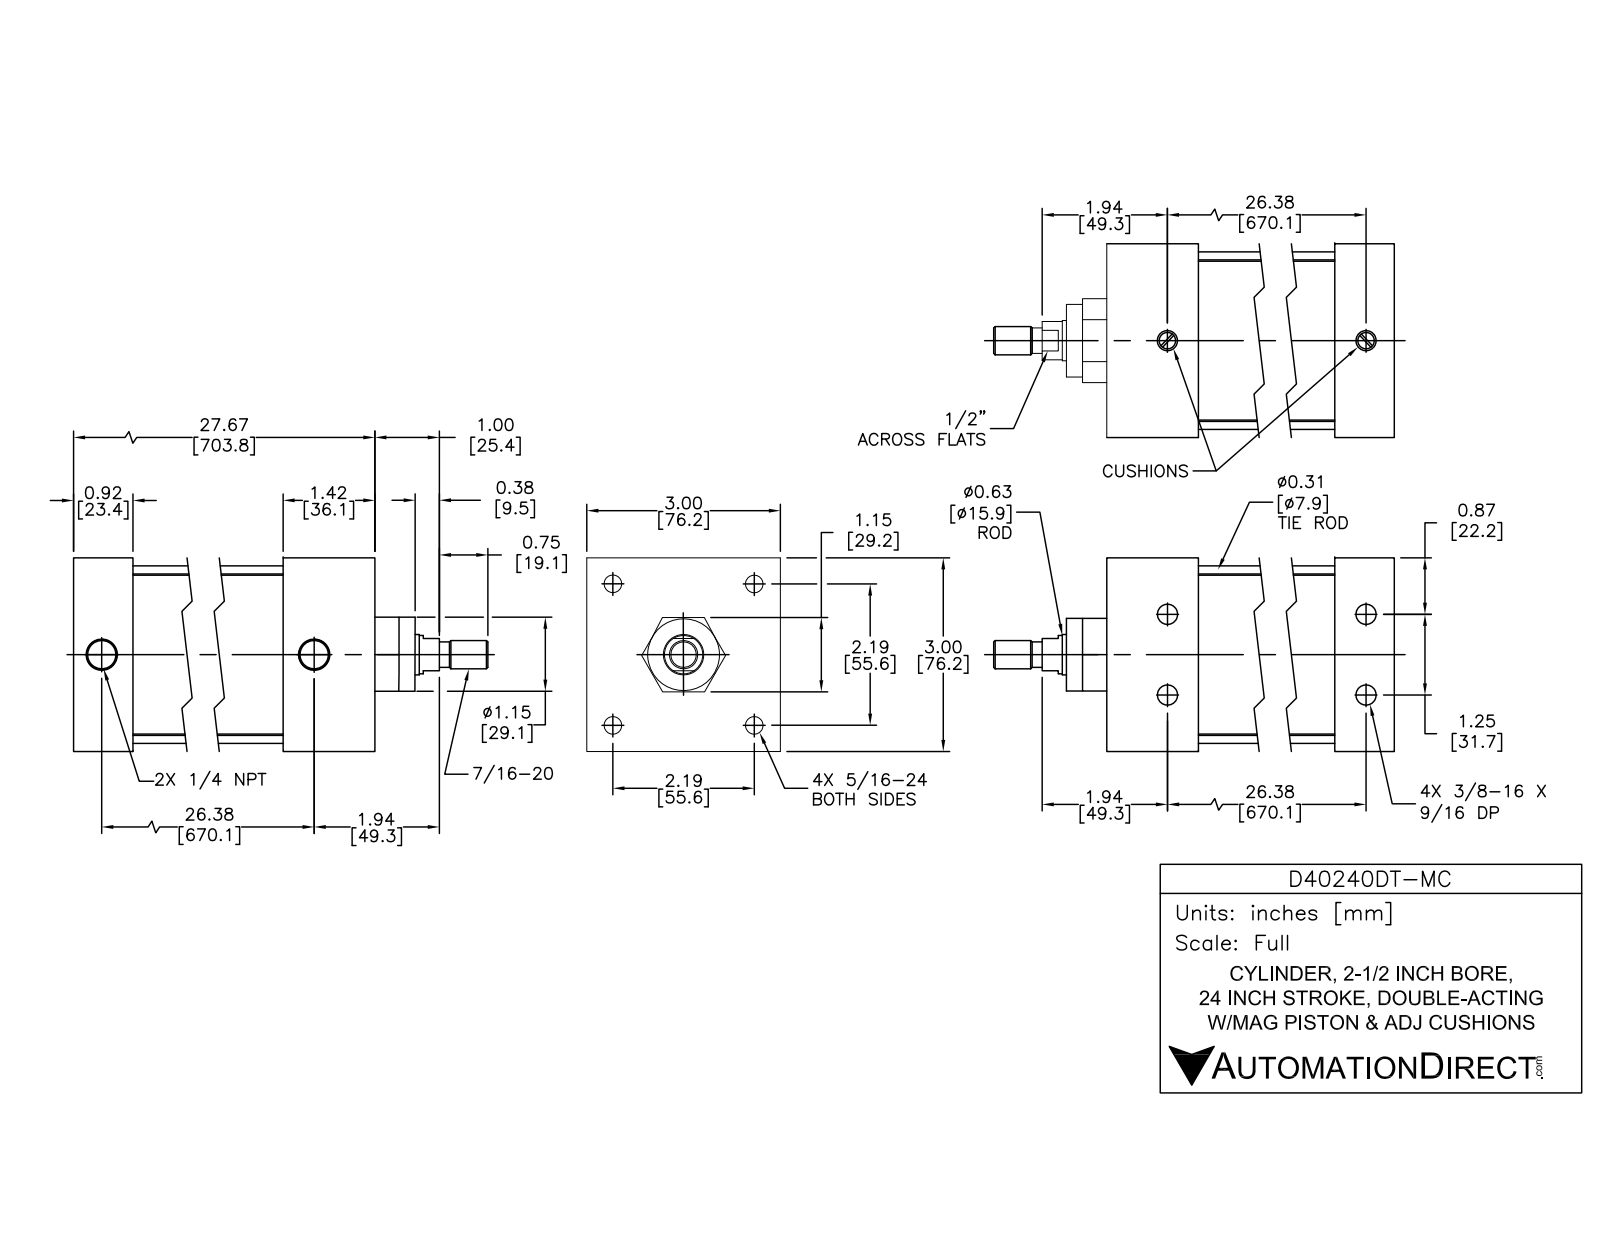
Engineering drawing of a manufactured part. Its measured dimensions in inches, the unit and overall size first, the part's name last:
Units: inches
Overall size (bounding box): 29.496 × 3 × 3
Round holes (diameter × count): ⌀0.267 ×4, ⌀0.307 ×4, ⌀0.359 ×4, ⌀0.5 ×4, ⌀0.297 ×2, ⌀0.477 ×2, ⌀0.625 ×1, ⌀0.628 ×1, ⌀2.5 ×1
Round bosses / shafts (diameter × count): ⌀0.484 ×4, ⌀0.313 ×4, ⌀0.282 ×4, ⌀2.75 ×1, ⌀2.497 ×1, ⌀1.12 ×1, ⌀0.622 ×1, ⌀0.59 ×1
Partial cylindrical surfaces — rounded edges, fillets, slot ends (radius × count): R0.3 ×4
Main face-to-face distances: 3, 27.746, 26.726, 1.02, 1.42, 25.306, 26.326, 1, 26.826, 25.406
Hole centre spacings: 1.556, 2.2, 26.378, 26.37, 0.625, 0.625, 1.25, 3.111
Volume: 67.24 in³ · Surface area: 680.5 in²
Bodies: 12 solids, 298 faces (94 planar, 114 cylindrical, 90 other)
Part name (STEP PRODUCT): D40240DT-MC; D40240DT-M PISTON; D40240DT-M BODY
STEP written by: SolidWorks 2015 (AUTOMOTIVE_DESIGN)
